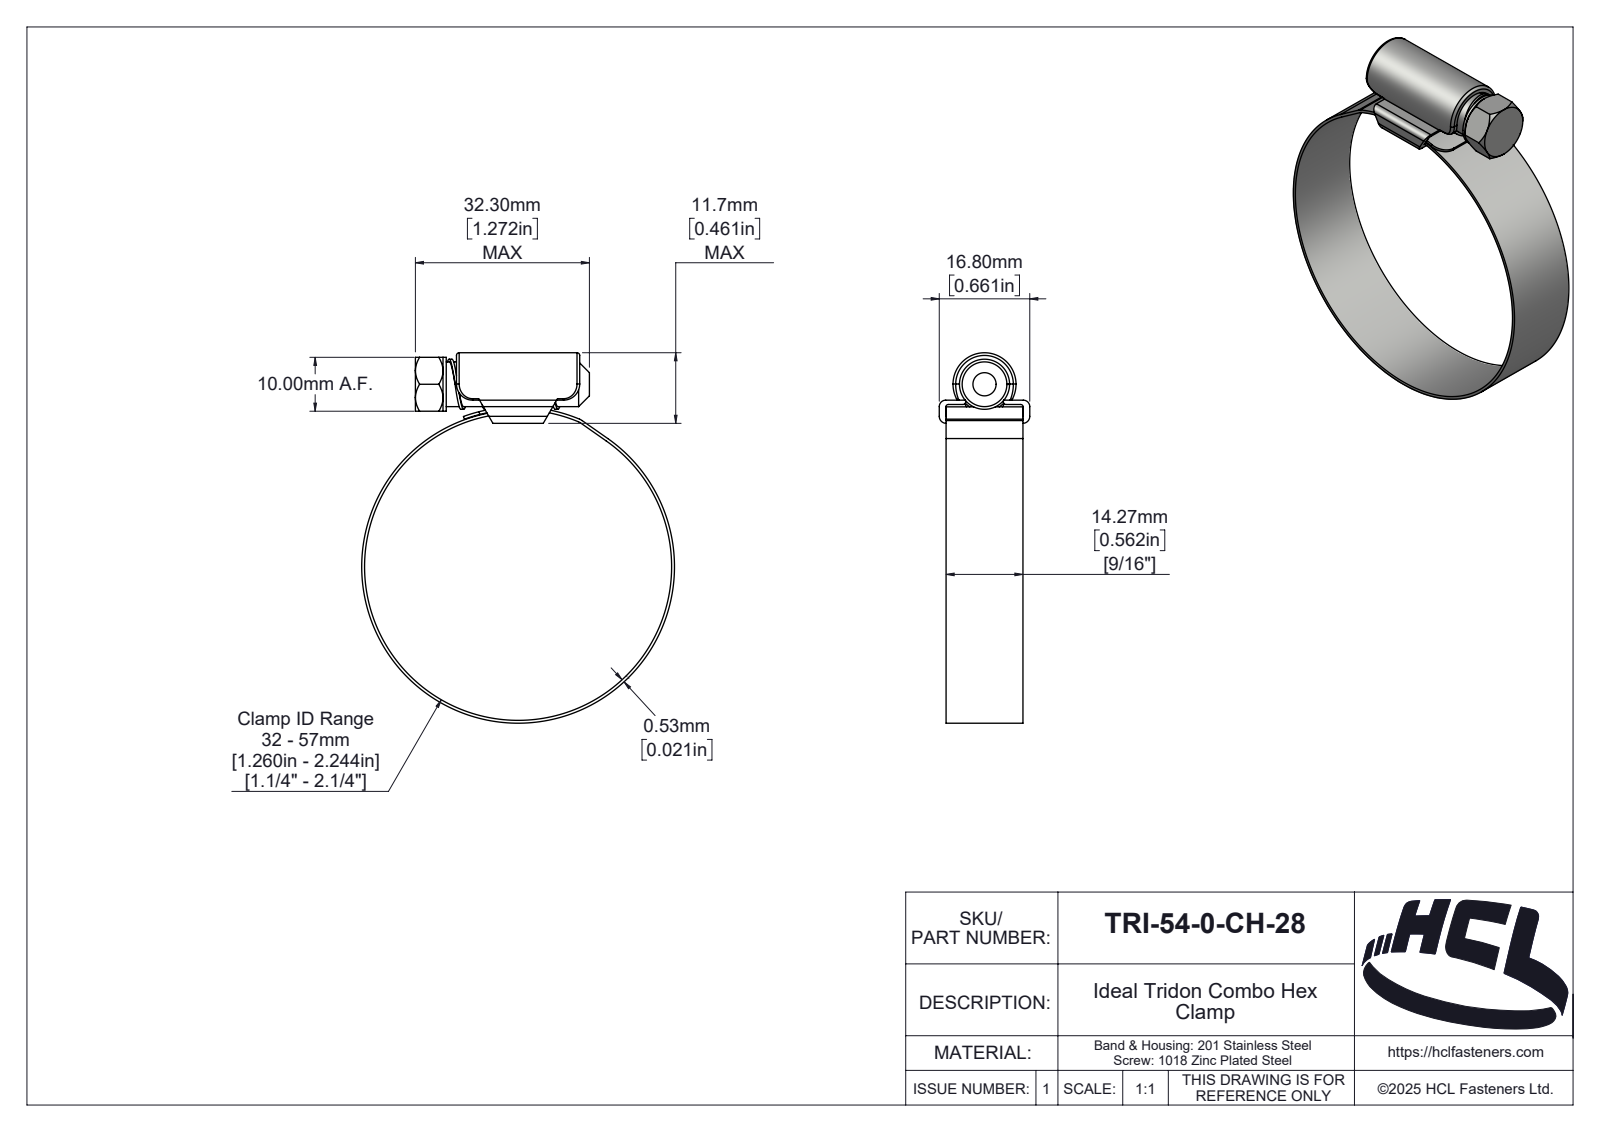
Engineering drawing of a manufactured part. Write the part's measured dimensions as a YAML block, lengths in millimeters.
part_name: "TRI-54-0-CH-28"
step_written_by: "SolidWorks 2025 (AUTOMOTIVE_DESIGN)"
units: millimeters
bodies: {solids: 3, faces: 212, planar: 35, cylindrical: 101, other: 76}
overall_size: [68.73, 58.06, 16.8]
volume: 4332
surface_area: 8647
round_holes:
  - {diameter: 57, count: 1}
round_bosses_or_shafts:
  - {diameter: 58.06, count: 1}
  - {diameter: 10, count: 1}
  - {diameter: 8.3, count: 1}
partial_cylinders:
  - {radius: 0.5, count: 6}
  - {radius: 3, count: 4}
  - {radius: 0.1, count: 2}
  - {radius: 1.2, count: 2}
  - {radius: 1.3, count: 2}
  - {radius: 0.46, count: 1}
  - {radius: 1.89, count: 1}
  - {radius: 2, count: 1}
face_to_face_distances: [1.2, 14.26, 0.53, 3.5, 2.3, 4.3, 3.1, 0.8, 9.99, 1.27]
